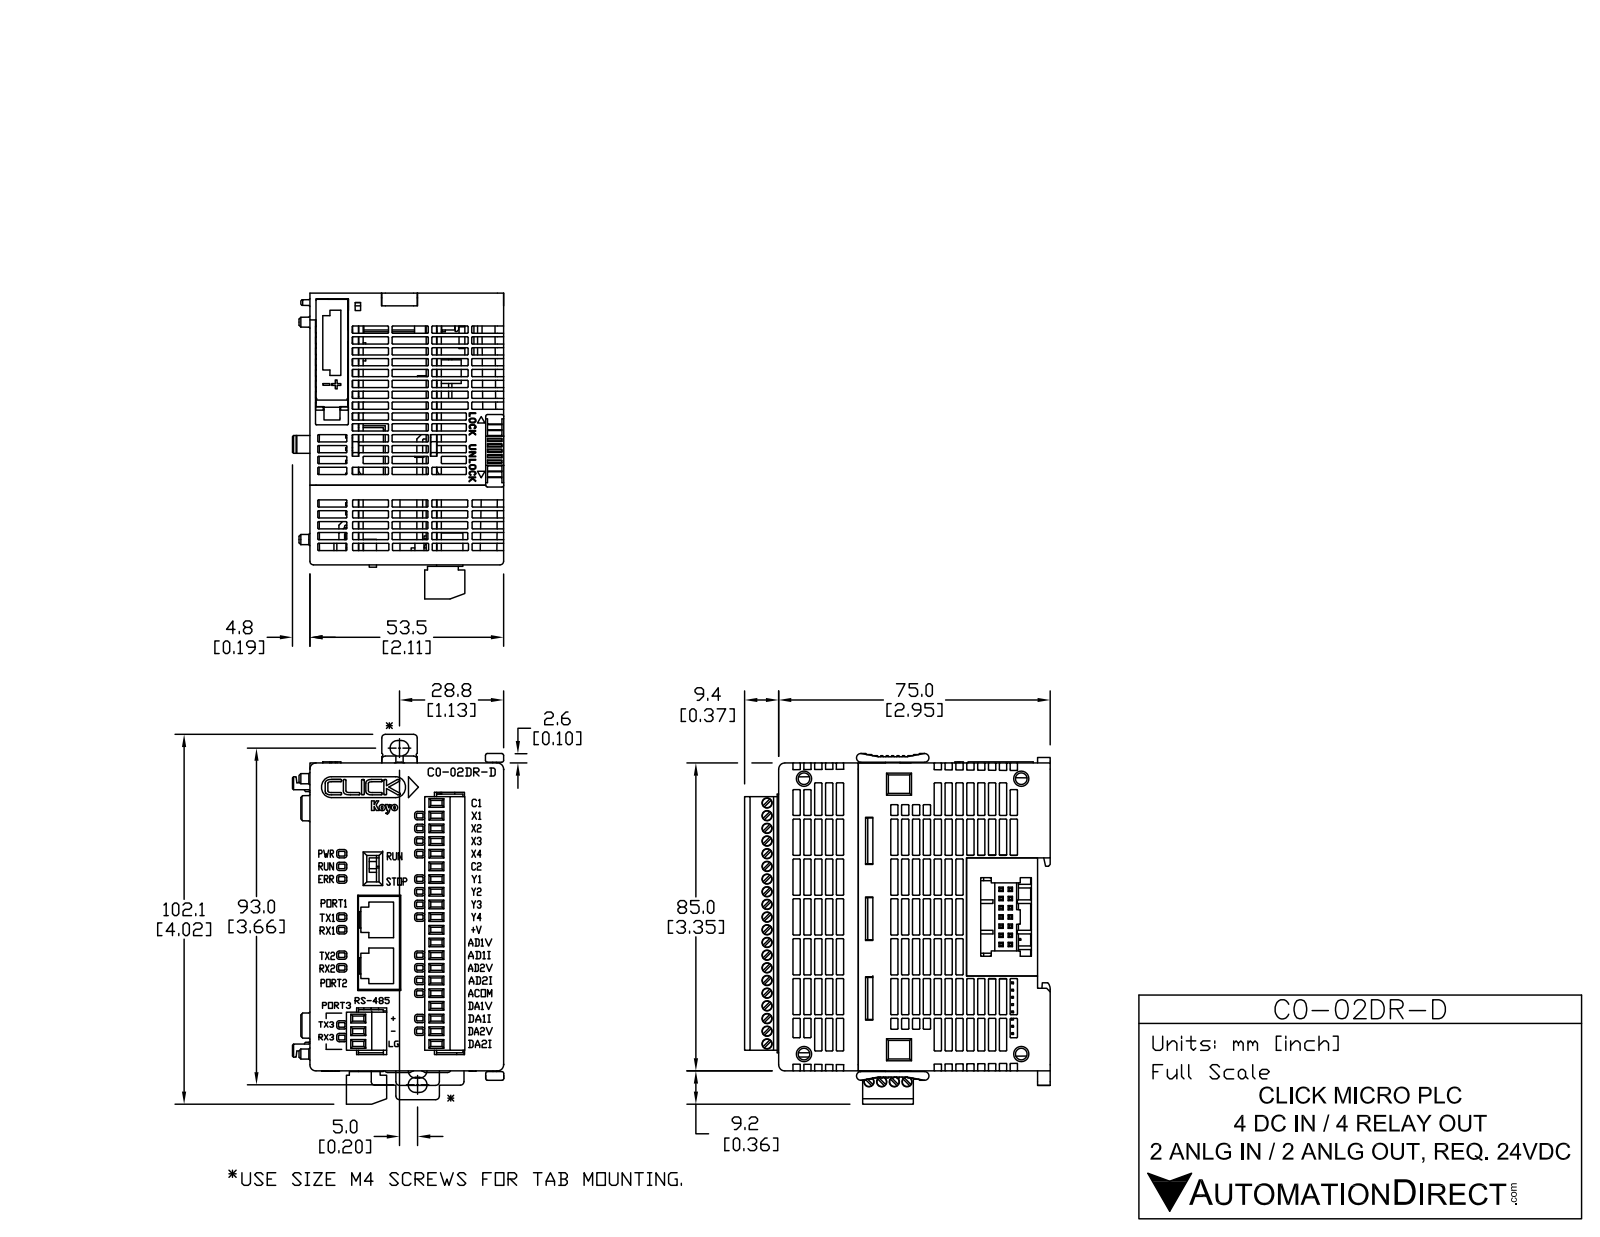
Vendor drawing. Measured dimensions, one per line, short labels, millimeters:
name: C0-02DR-D
written by: SolidWorks 2009 (AUTOMOTIVE_DESIGN)
unit: mm
bodies: 1 solid, 6070 faces (4092 planar, 1797 cylindrical, 181 other)
size: 96.8 × 84.4 × 58.35
volume: 332 445 mm³; area: 47 010 mm²
holes: 27× ⌀1, 27× ⌀2.8, 1× ⌀1.75, 1× ⌀1.85, 1× ⌀2.2
bosses: 27× ⌀2.6, 2× ⌀2.8, 2× ⌀2.15, 1× ⌀1.9
rounds: 867× R0.2, 67× R0.3, 39× R0.5, 27× R2.8, 11× R1, 7× R1.2, 6× R1.7, 5× R0.1
face distances: 0.5, 53, 71.5, 53.5, 84.5, 85, 52.5, 3.5, 84, 75
hole spacings: 3.5, 7, 10.5, 14, 17.5, 21, 24.5, 28
